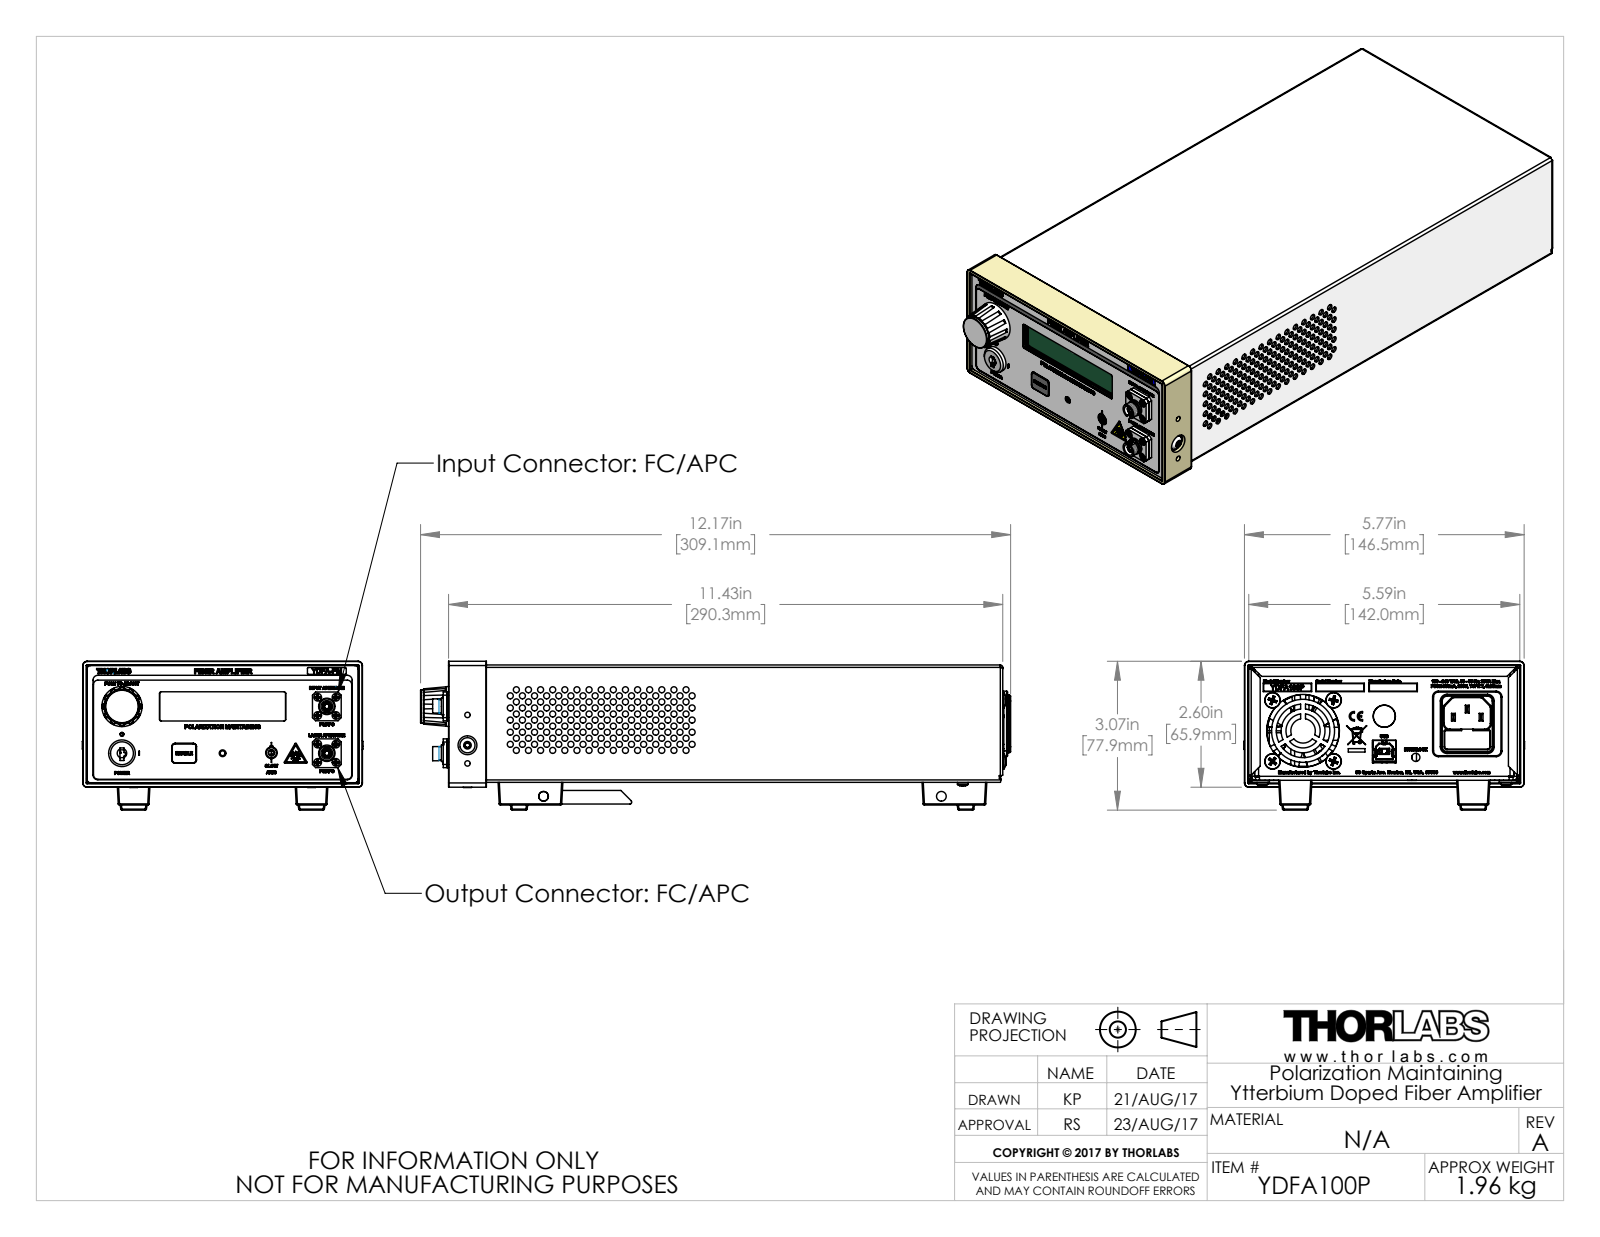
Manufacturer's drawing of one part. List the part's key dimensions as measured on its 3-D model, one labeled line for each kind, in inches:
Part name (STEP PRODUCT): TTN137123-E0W
STEP written by: SolidWorks 2016 (AUTOMOTIVE_DESIGN)
Units: inches
Bodies: 0 solids, 9222 faces (4783 planar, 2099 cylindrical, 2340 other)
Overall size (bounding box): 12.17 × 5.786 × 3.069
Round holes (diameter × count): ⌀0.125 ×171, ⌀0.037 ×42, ⌀0.039 ×16, ⌀0.097 ×12, ⌀0.157 ×12, ⌀0.12 ×9, ⌀0.07 ×8, ⌀0.087 ×8, ⌀0.087 ×8, ⌀0.112 ×8, ⌀0.122 ×8, ⌀0.165 ×8
Round bosses / shafts (diameter × count): ⌀0.165 ×12, ⌀0.161 ×12, ⌀0.153 ×12, ⌀0.167 ×8, ⌀0.164 ×8, ⌀0.12 ×8, ⌀0.086 ×8, ⌀0.018 ×6
Partial cylindrical surfaces — rounded edges, fillets, slot ends (radius × count): R0.02 ×51, R0.025 ×48, R0.005 ×32, R0.01 ×20, R0.05 ×17, R0.01 ×15, R0.118 ×14, R0.039 ×12
Main face-to-face distances: 0.04, 0.062, 2.377, 2.337, 2.276, 2.315, 5.55, 0.057, 0.018, 5.532
Hole centre spacings: 0.559, 0.25, 0.5, 0.354, 0.791, 0.902, 0.75, 0.707
